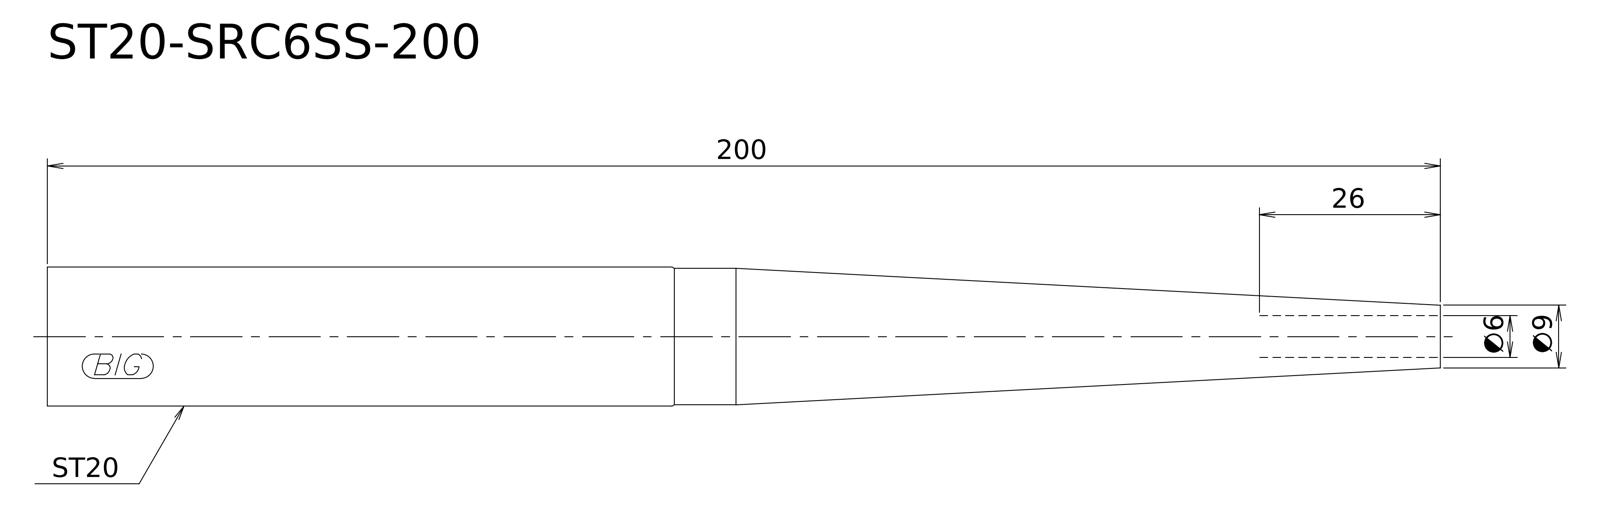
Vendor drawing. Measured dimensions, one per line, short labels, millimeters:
written by: Kubotek KeyCreator V8.5.1 (14335) (CONFIG_CONTROL_DESIGN)
unit: mm
bodies: 1 solid, 6 faces (2 planar, 2 cylindrical, 2 other)
size: 200 × 20 × 20
volume: 47 934 mm³; area: 11 131 mm²
bosses: 1× ⌀20, 1× ⌀19.6
face distances: 200
